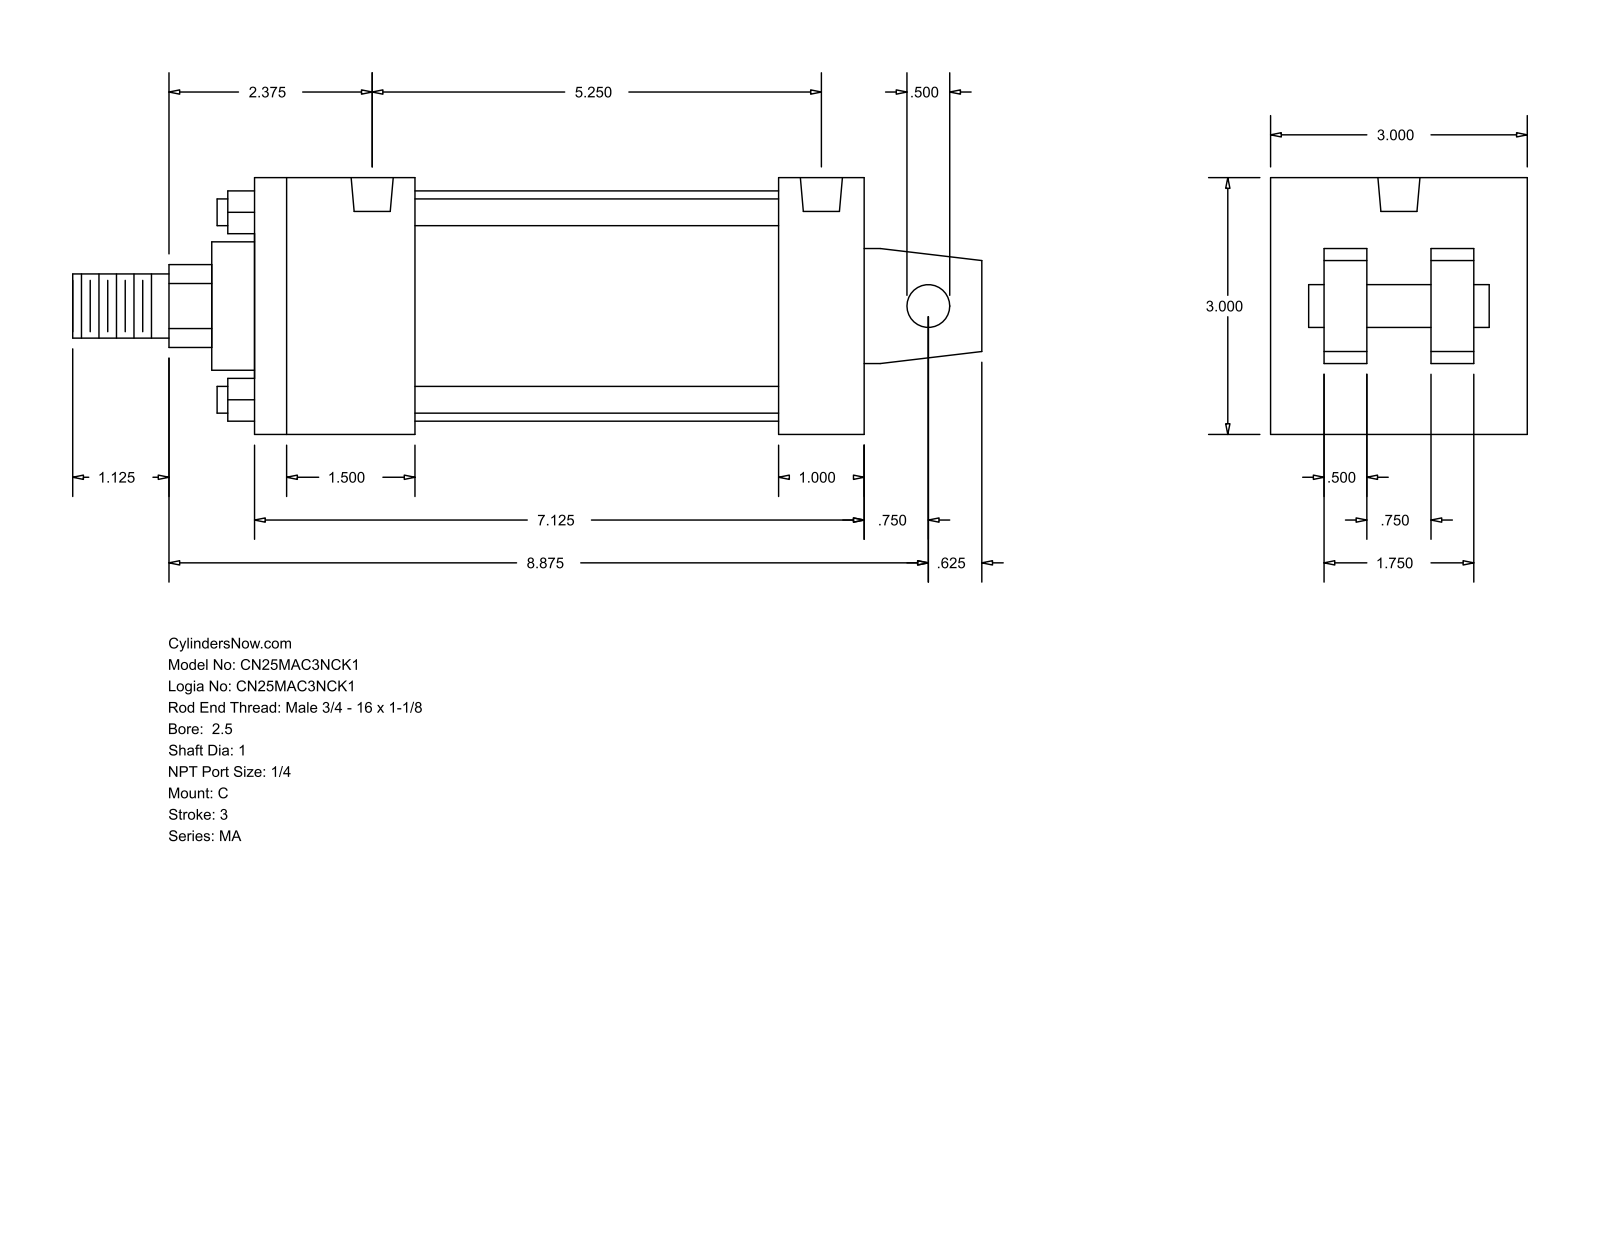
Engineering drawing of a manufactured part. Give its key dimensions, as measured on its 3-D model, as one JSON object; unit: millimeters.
{"part_name": "MA_C__0250_1", "step_written_by": "GSSL Pune (CONFIG_CONTROL_DESIGN)", "units": "millimeters", "bodies": {"solids": 0, "faces": 103, "planar": 76, "cylindrical": 27, "other": 0}, "overall_size": [269.88, 76.2, 76.2], "round_holes": [[7.94, 4], [12.49, 2]], "round_bosses_or_shafts": [[7.94, 4], [68.33, 1], [38.1, 1], [25.4, 1], [19.05, 1], [12.7, 1]], "partial_cylinders_radius": [[12.29, 1]], "face_to_face_distances": [76.2, 47.63, 180.98, 12.7, 60.33, 15.87, 28.57, 155.57, 107.94, 133.35], "hole_center_spacings": [133.35]}
